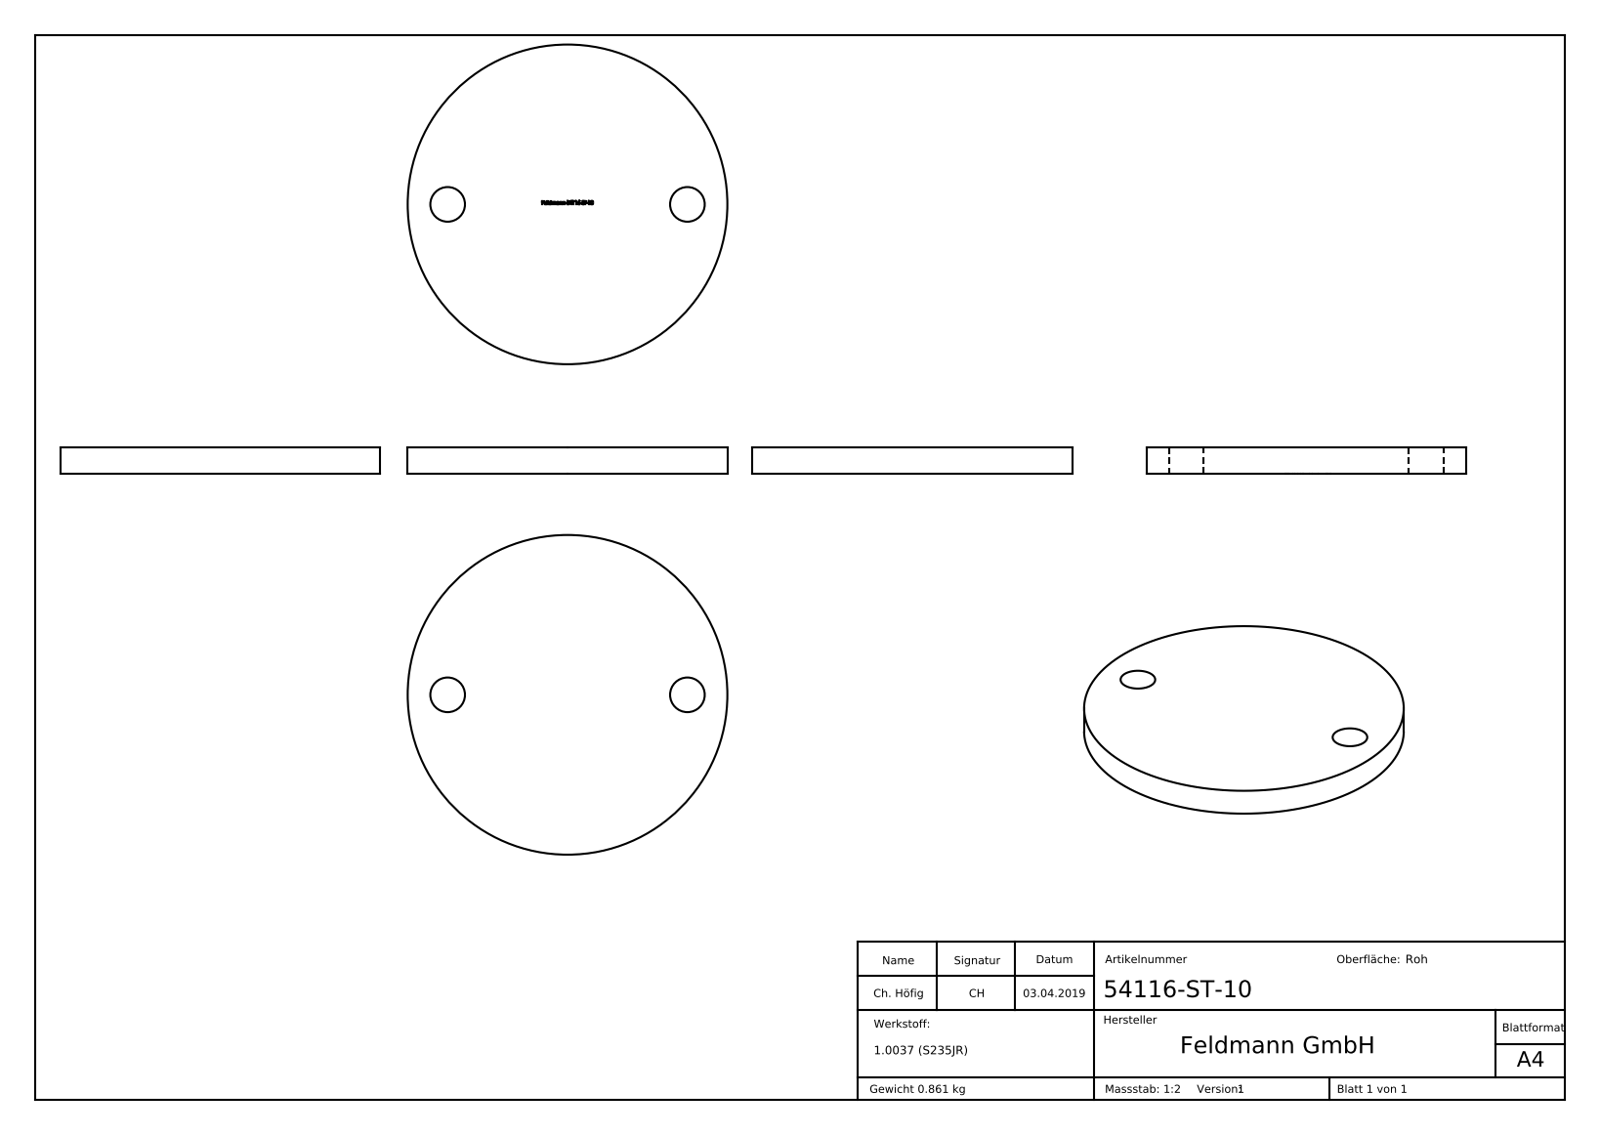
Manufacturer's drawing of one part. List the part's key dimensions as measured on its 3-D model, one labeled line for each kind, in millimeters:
Part name (STEP PRODUCT): 54116-ST-10
STEP written by: SolidWorks 2015 (CONFIG_CONTROL_DESIGN)
Units: millimetres
Bodies: 1 solid, 234 faces (139 planar, 6 cylindrical, 89 other)
Overall size (bounding box): 120 × 120 × 10
Volume: 110 442 mm³ · Surface area: 26 685 mm²
Round holes (diameter × count): ⌀13 ×2
Round bosses / shafts (diameter × count): ⌀120 ×1
Main face-to-face distances: 10, 9.9, 1.01, 9.72, 10.73, 15.65, 5.93, 4.92, 0.88, 2.02
Hole centre spacings: 90
